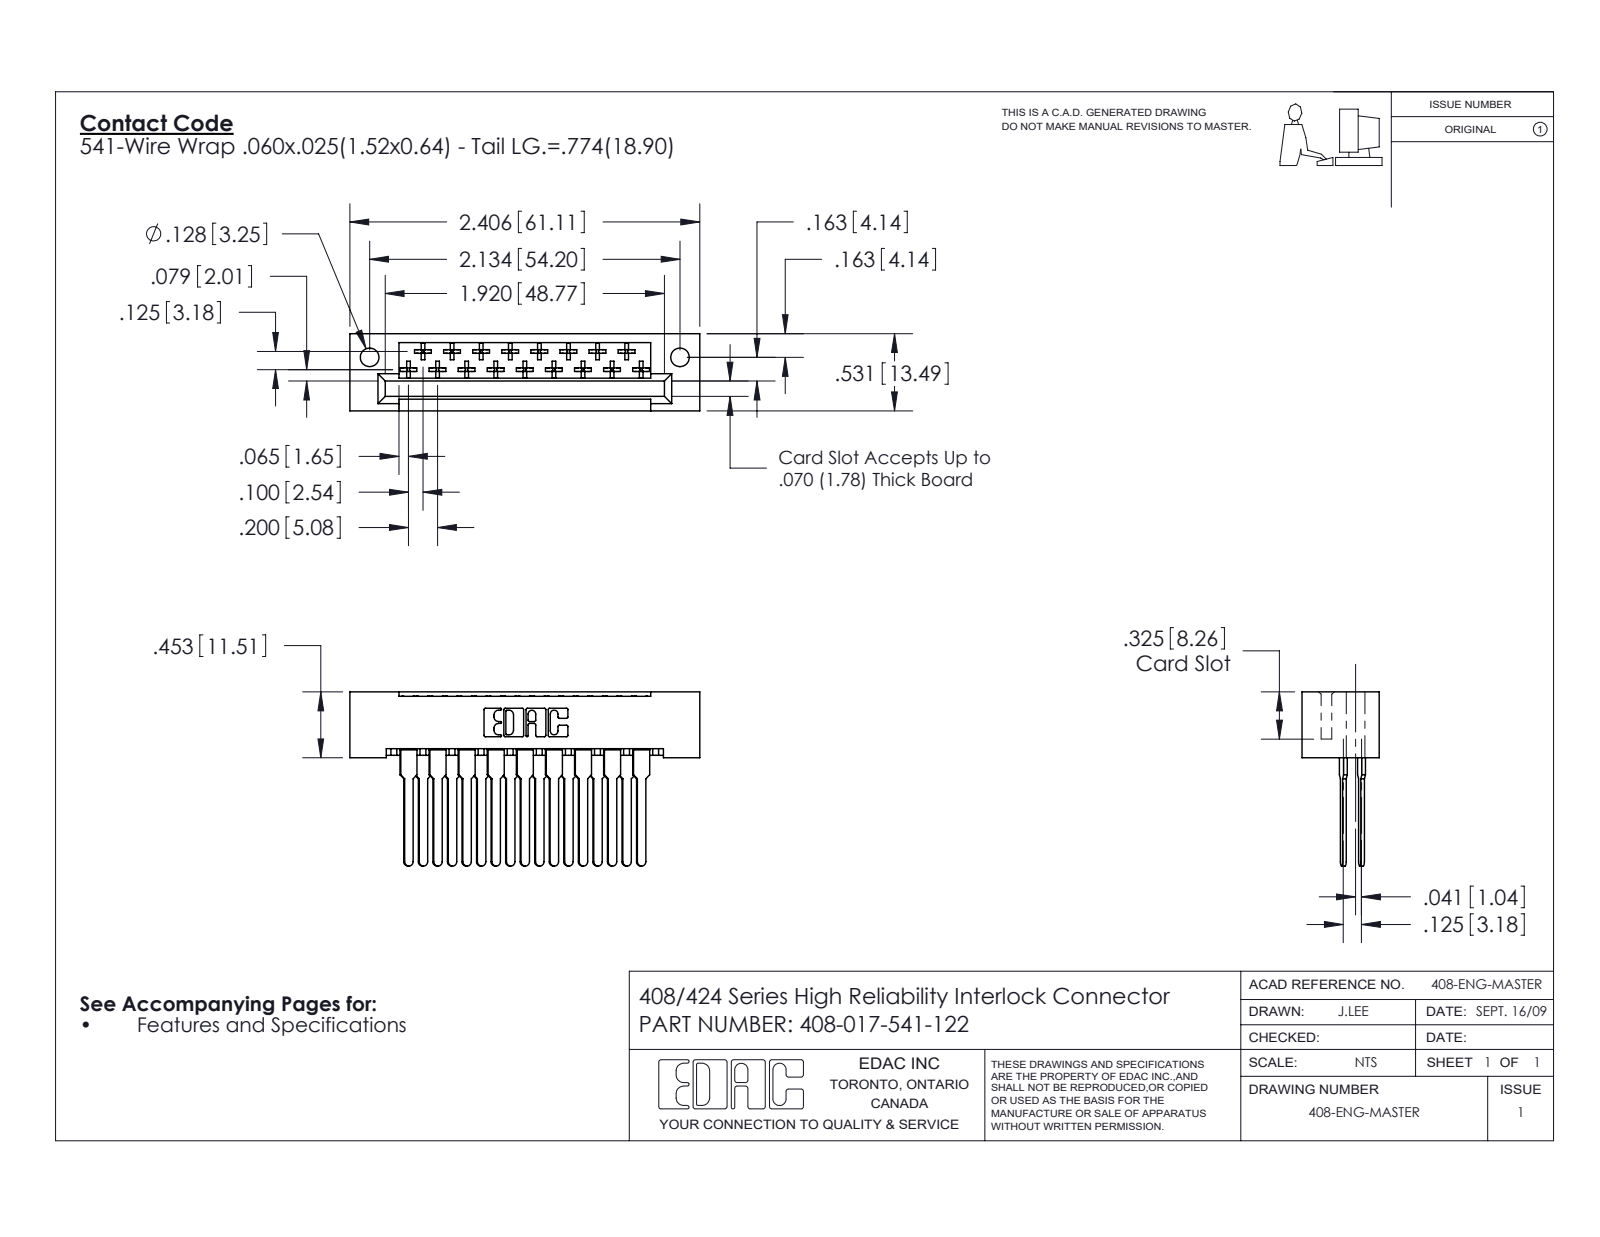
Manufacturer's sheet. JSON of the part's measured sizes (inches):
{"part_name": "408 Part_017 - 1; 408-290-001_408-290-141; 408-017-541-122", "step_written_by": "SolidWorks 2016 (CONFIG_CONTROL_DESIGN)", "units": "inches", "bodies": {"solids": 18, "faces": 1028, "planar": 759, "cylindrical": 201, "other": 68}, "overall_size": [2.406, 1.197, 0.531], "volume_in3": 0.439, "surface_area_in2": 14.21, "round_holes": [[0.128, 2]], "partial_cylinders_radius": [[0.01, 102], [0.01, 22], [0.02, 19], [0.03, 17], [0.007, 6], [0.031, 6], [0.026, 3]], "face_to_face_distances": [0.1, 0.296, 0.025, 0.531, 0.025, 0.125, 0.104, 0.235, 0.259, 0.272], "hole_center_spacings": [2.134]}
